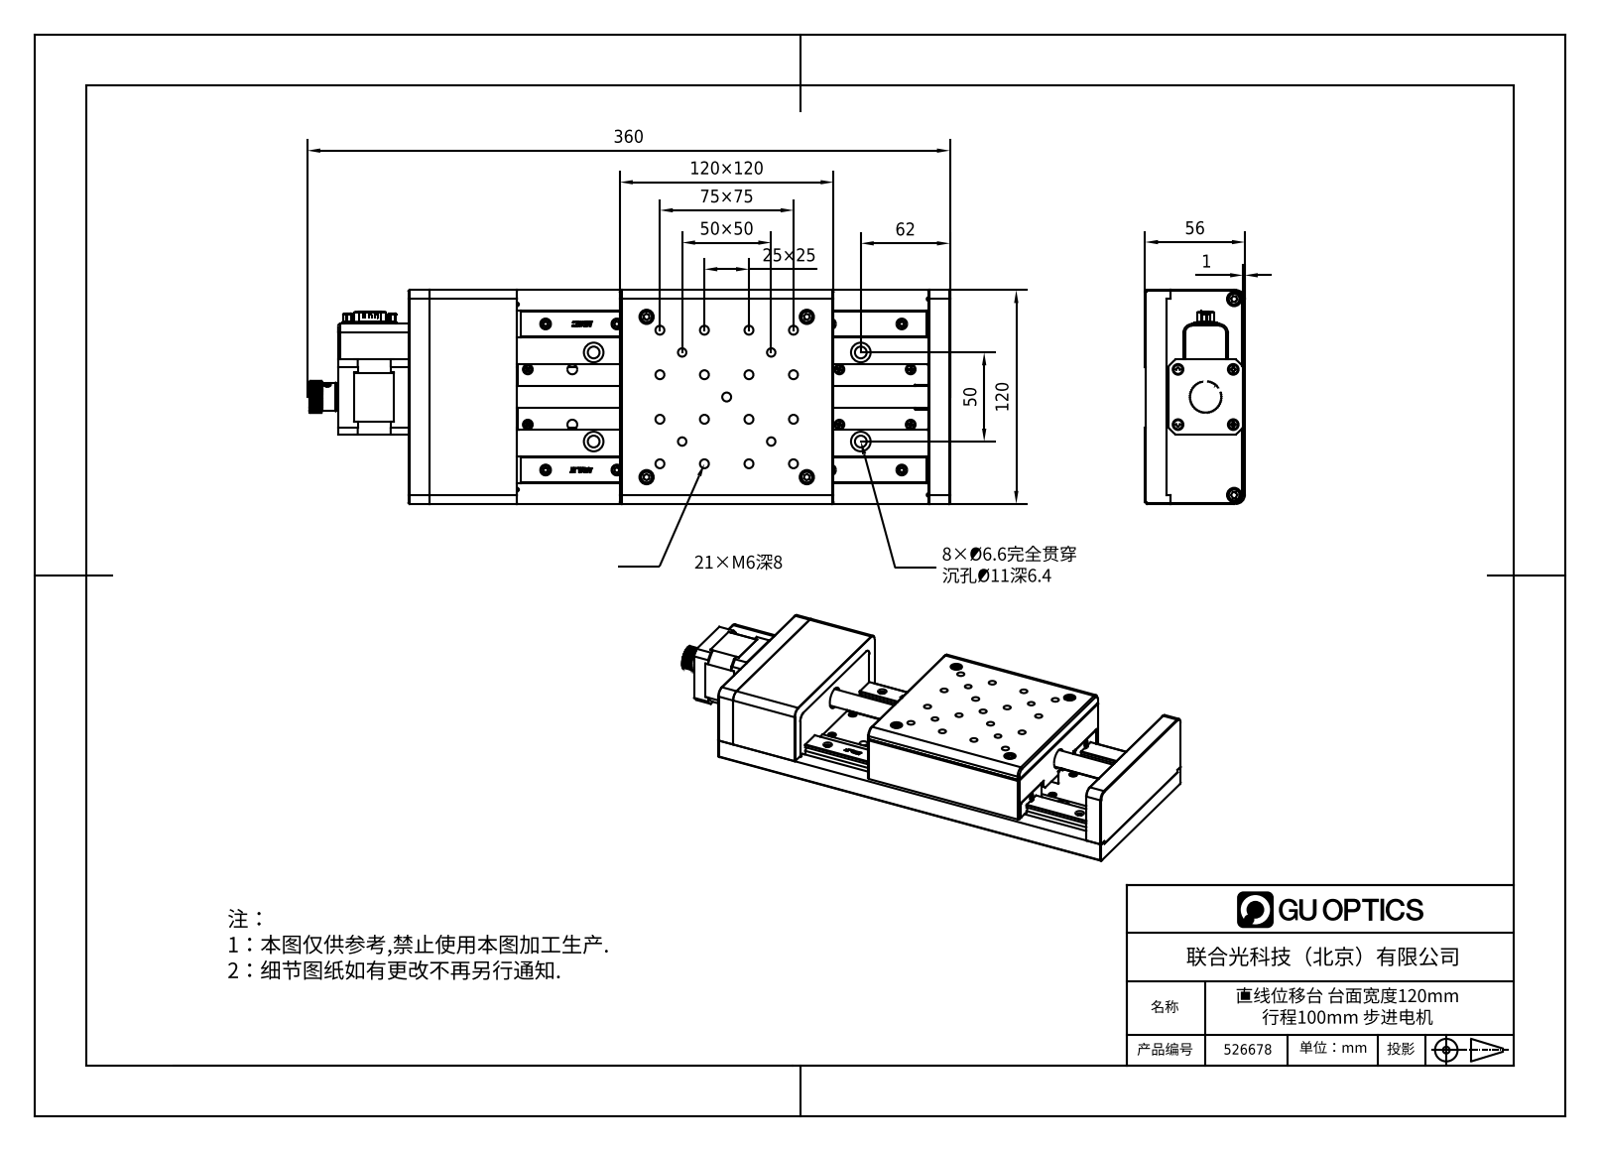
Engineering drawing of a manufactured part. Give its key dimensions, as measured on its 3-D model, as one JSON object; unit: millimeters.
{"part_name": "FMS120V-100", "step_written_by": "SolidWorks 2017 (CONFIG_CONTROL_DESIGN)", "units": "millimeters", "bodies": {"solids": 0, "faces": 842, "planar": 411, "cylindrical": 270, "other": 161}, "overall_size": [352, 120, 56], "round_holes": [[5, 17], [8, 14], [6.6, 8], [6, 6], [2, 5], [4.71, 4], [11, 4], [2.5, 2], [4.5, 2], [14, 1]], "round_bosses_or_shafts": [[1, 9], [4.4, 6], [5.5, 4], [7, 2], [4.2, 2], [12, 1]], "partial_cylinders_radius": [[0.5, 24], [1, 14], [0.4, 7], [5, 6], [0.3, 4], [1.5, 4], [20, 1], [20.5, 1]], "face_to_face_distances": [14, 34, 8, 28, 42, 48, 56, 120, 1, 13.7], "hole_center_spacings": [50, 25, 70.71, 35.36, 90, 100, 111.8, 15.9]}
